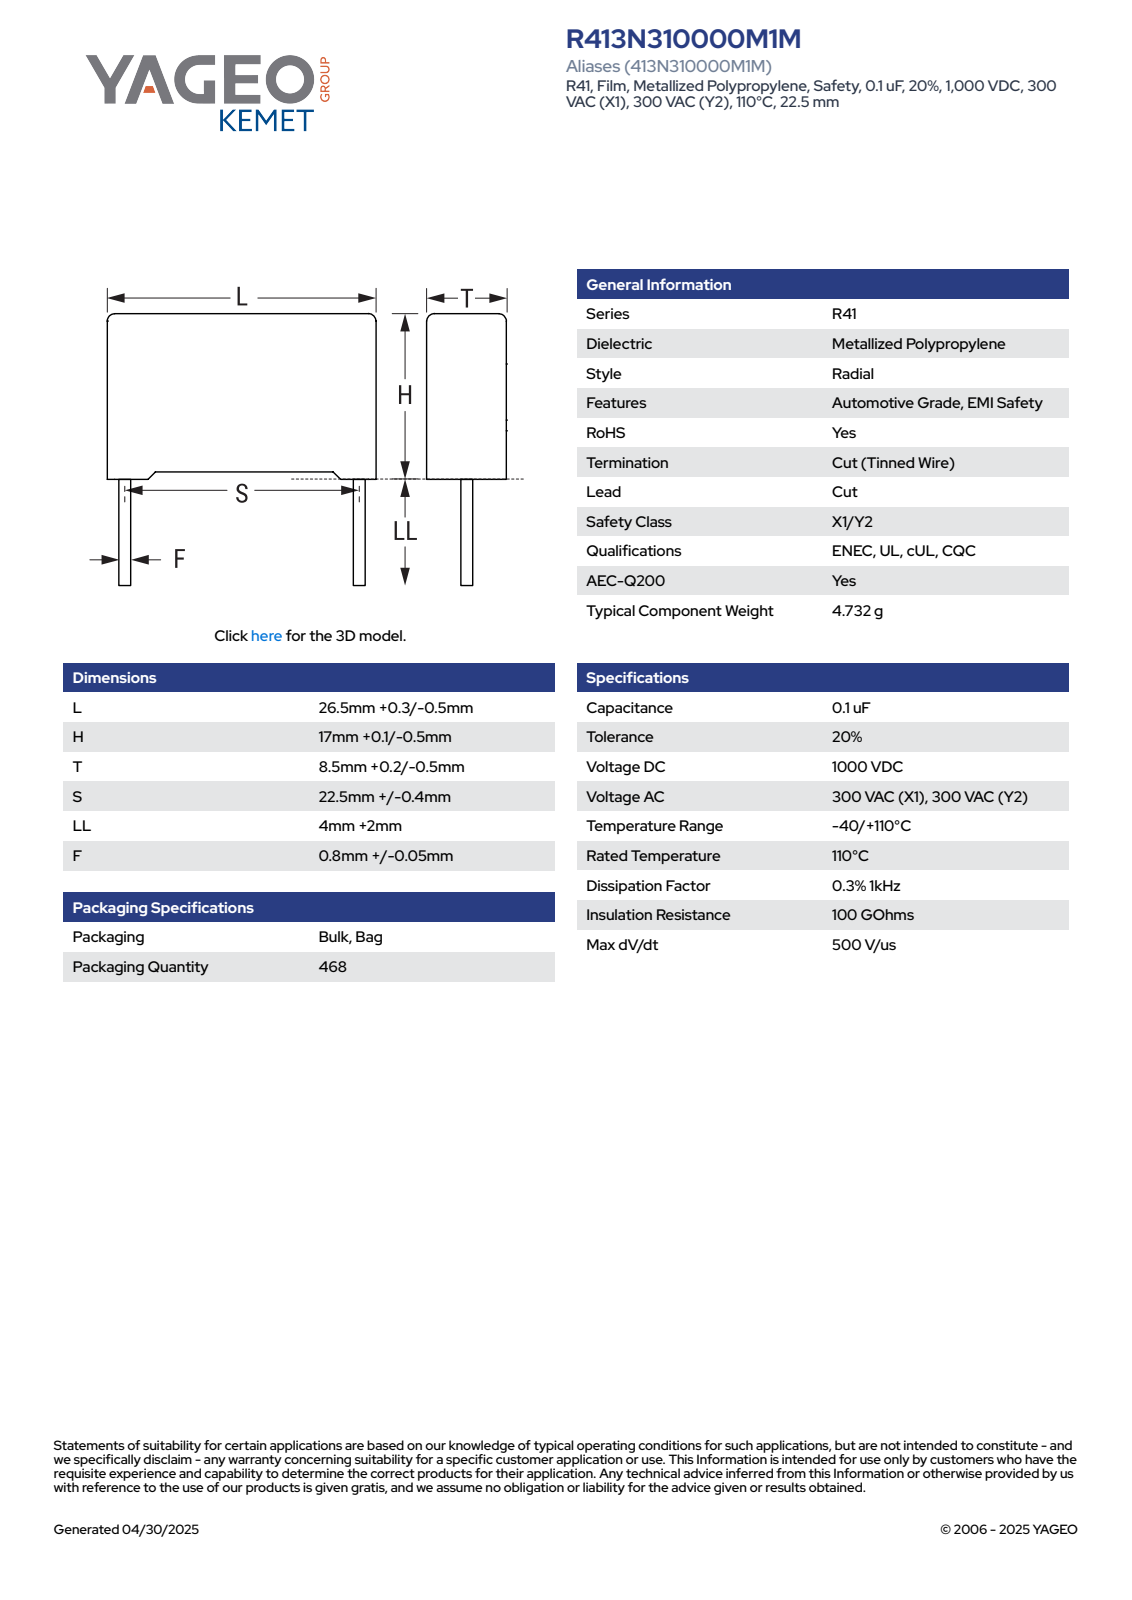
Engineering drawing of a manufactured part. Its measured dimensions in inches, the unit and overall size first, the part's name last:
Units: inches
Overall size (bounding box): 1.055 × 0.909 × 0.343
Round bosses / shafts (diameter × count): ⌀0.033 ×2
Partial cylindrical surfaces — rounded edges, fillets, slot ends (radius × count): R0.02 ×4
Main face-to-face distances: 0.343, 0.644, 1.055, 0.65, 0.035, 0.03, 0.023, 0.673, 0.307, 0.343
Volume: 0.234 in³ · Surface area: 2.726 in²
Bodies: 4 solids, 85 faces (77 planar, 8 cylindrical, 0 other)
Part name (STEP PRODUCT): CFR_RB2_26.5X17X8.5_L26.8H17.1T8.7S22.5LL6F0.85
STEP written by: SolidWorks 2021 (AUTOMOTIVE_DESIGN)
